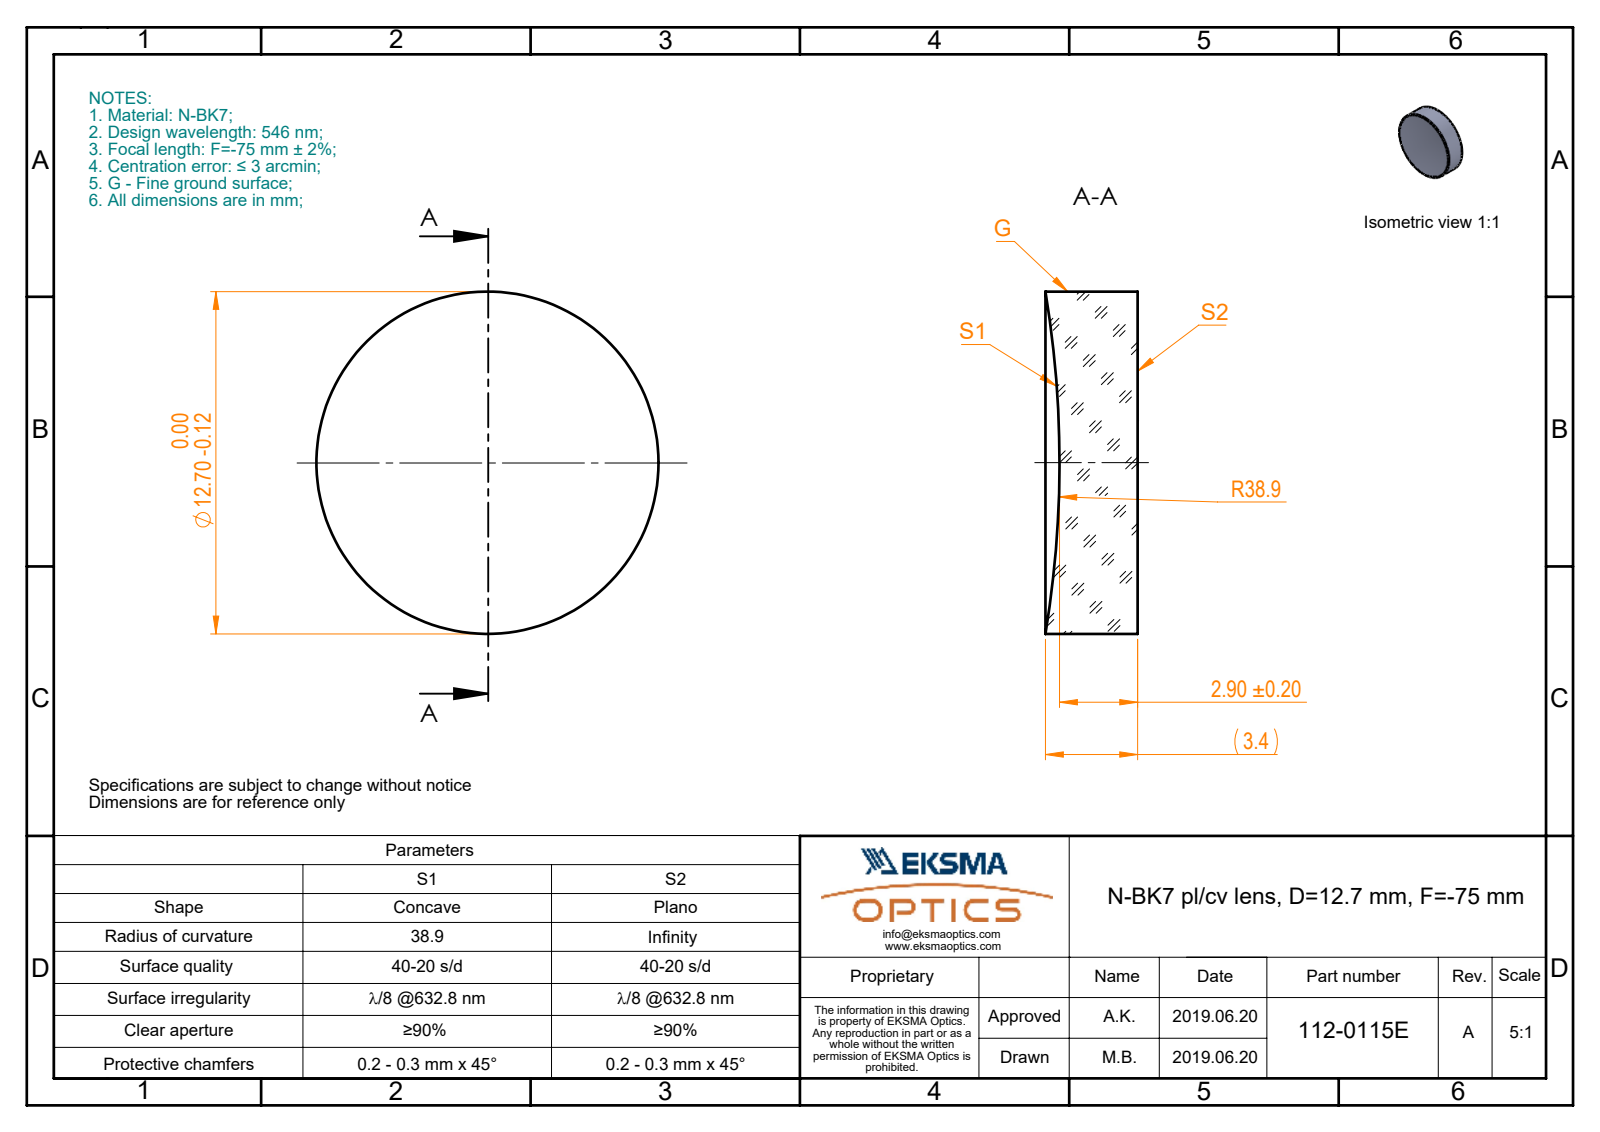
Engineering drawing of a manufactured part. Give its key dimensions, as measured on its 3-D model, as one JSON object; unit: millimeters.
{"part_name": "112-0115E BK7 pl-cv 12.7 F-75", "step_written_by": "SolidWorks 2017 (CONFIG_CONTROL_DESIGN)", "units": "millimeters", "bodies": {"solids": 1, "faces": 5, "planar": 1, "cylindrical": 2, "other": 2}, "overall_size": [12.7, 12.7, 3.42], "volume_mm3": 400, "surface_area_mm2": 391, "round_bosses_or_shafts": [[12.7, 1]]}
